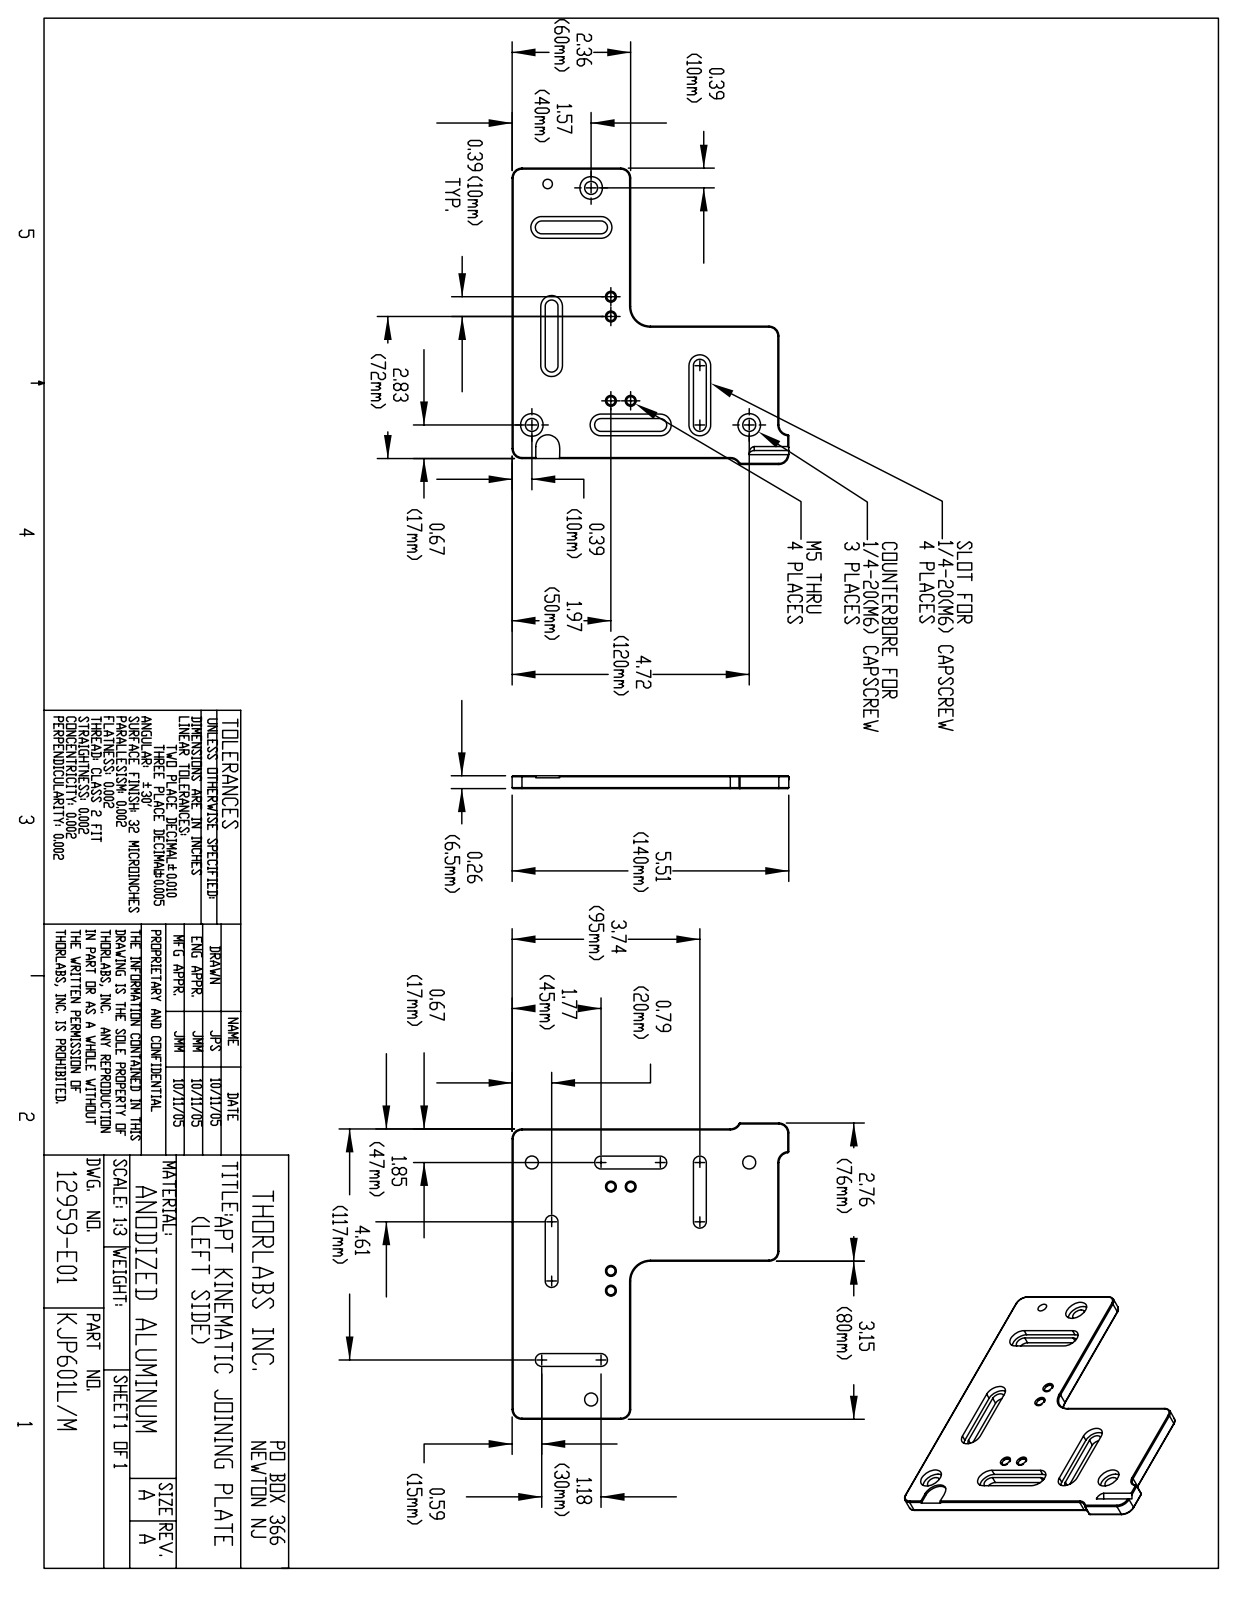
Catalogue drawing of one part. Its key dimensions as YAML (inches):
part_name: "12959-E0W"
step_written_by: "SolidWorks 2007 (AUTOMOTIVE_DESIGN)"
units: inches
bodies: {solids: 0, faces: 146, planar: 38, cylindrical: 70, other: 38}
overall_size: [5.906, 5.512, 0.256]
round_holes:
  - {diameter: 0.165, count: 4}
  - {diameter: 0.26, count: 3}
  - {diameter: 0.453, count: 3}
partial_cylinders:
  - {radius: 0.02, count: 18}
  - {radius: 0.128, count: 8}
  - {radius: 0.217, count: 8}
  - {radius: 0.197, count: 7}
  - {radius: 0.098, count: 1}
  - {radius: 0.236, count: 1}
  - {radius: 0.394, count: 1}
face_to_face_distances: [0.256, 0.118, 0.138, 0.089, 0.344, 2.953, 3.937, 0.433, 2.362, 2.638]
hole_center_spacings: [0.394, 1.646, 1.681, 1.727, 2.026, 2.075, 2.112, 2.205]
